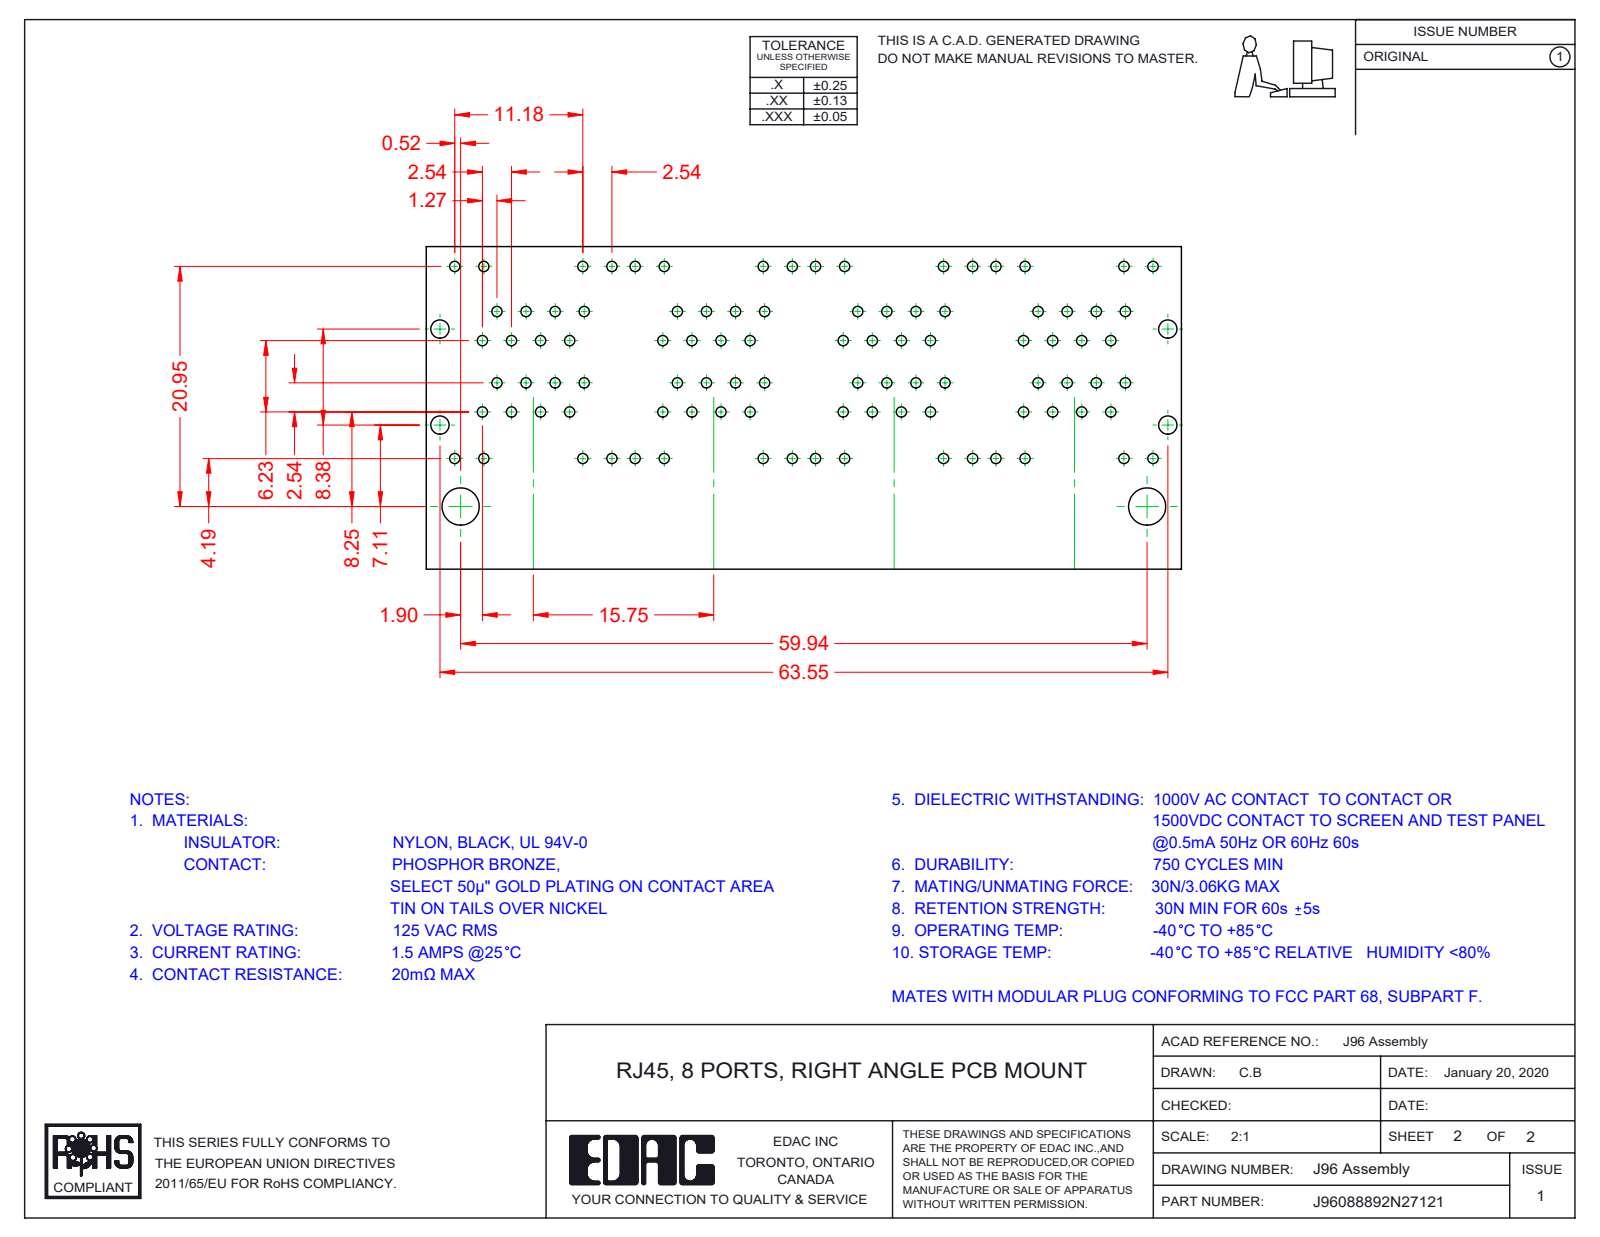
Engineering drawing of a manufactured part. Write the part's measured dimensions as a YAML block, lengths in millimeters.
part_name: "96 Shield_8 Ports LED - No EMI; 96 Contacts Lower; 96 Contacts Upper; 96 Contact Lock Lower (+8 more)"
step_written_by: "SolidWorks 2016 (CONFIG_CONTROL_DESIGN)"
units: millimeters
bodies: {solids: 96, faces: 7658, planar: 6069, cylindrical: 1323, other: 266}
overall_size: [64.05, 29.58, 28.68]
volume: 24160
surface_area: 63658
round_holes:
  - {diameter: 1.7, count: 3}
round_bosses_or_shafts:
  - {diameter: 1.68, count: 3}
partial_cylinders:
  - {radius: 0.25, count: 124}
  - {radius: 0.35, count: 73}
  - {radius: 1, count: 72}
  - {radius: 0.5, count: 49}
  - {radius: 0.91, count: 32}
  - {radius: 0.2, count: 21}
  - {radius: 0.7, count: 11}
  - {radius: 0.22, count: 8}
face_to_face_distances: [15.75, 0.35, 9.95, 1.17, 1.6, 0.54, 9.98, 10.18, 12.67, 3.37]
hole_center_spacings: [15.75, 31.5]
